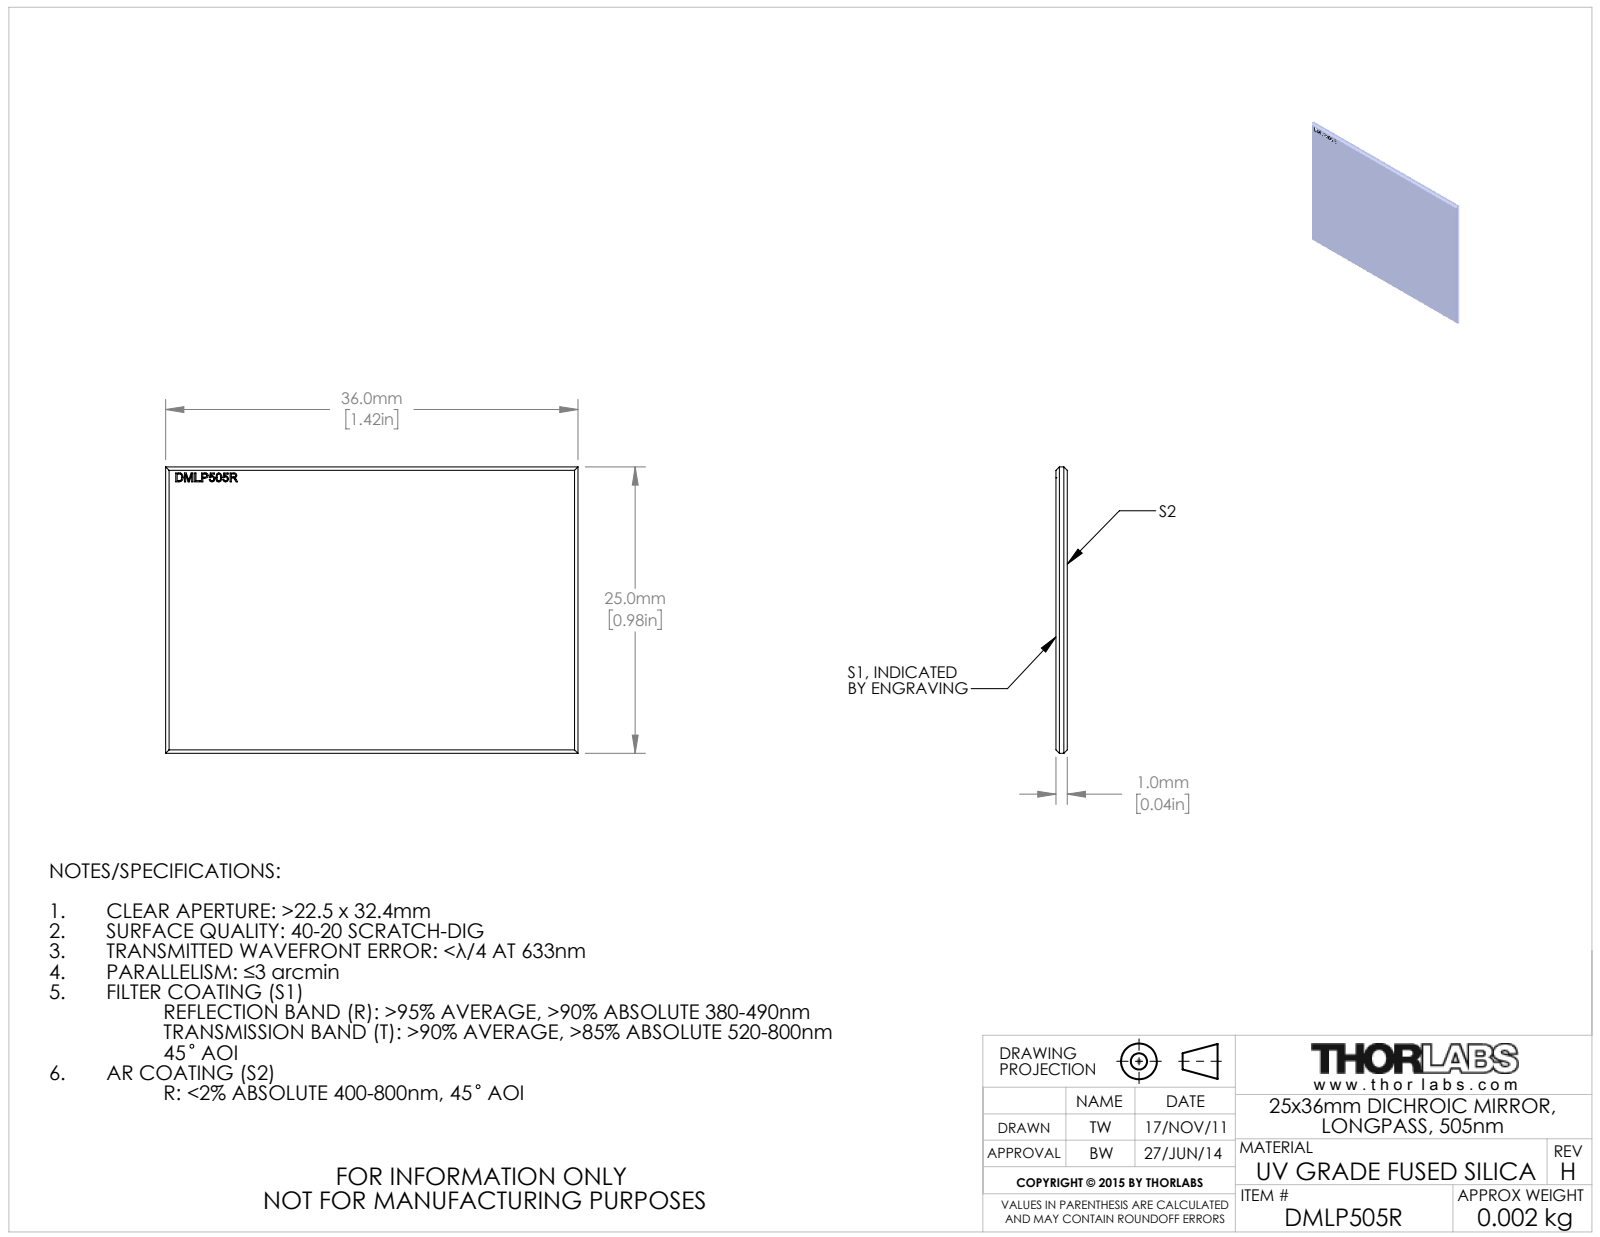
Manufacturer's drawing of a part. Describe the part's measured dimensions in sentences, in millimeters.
The part is named "21096-E0W". Its 3-D file was written by "SolidWorks 2018 (CONFIG_CONTROL_DESIGN)". It is 1 solid with 136 faces: 84 planar, 0 cylindrical and 52 other. Overall it measures 36 by 25 by 1 millimeters. Its volume is 889 cubic millimeters and its surface area 1 879 square millimeters. The main face-to-face distances are 1, 17.95, 17.96, 25, 25.74, 25.73, 36, 0.99, 0.75, 1.49.
